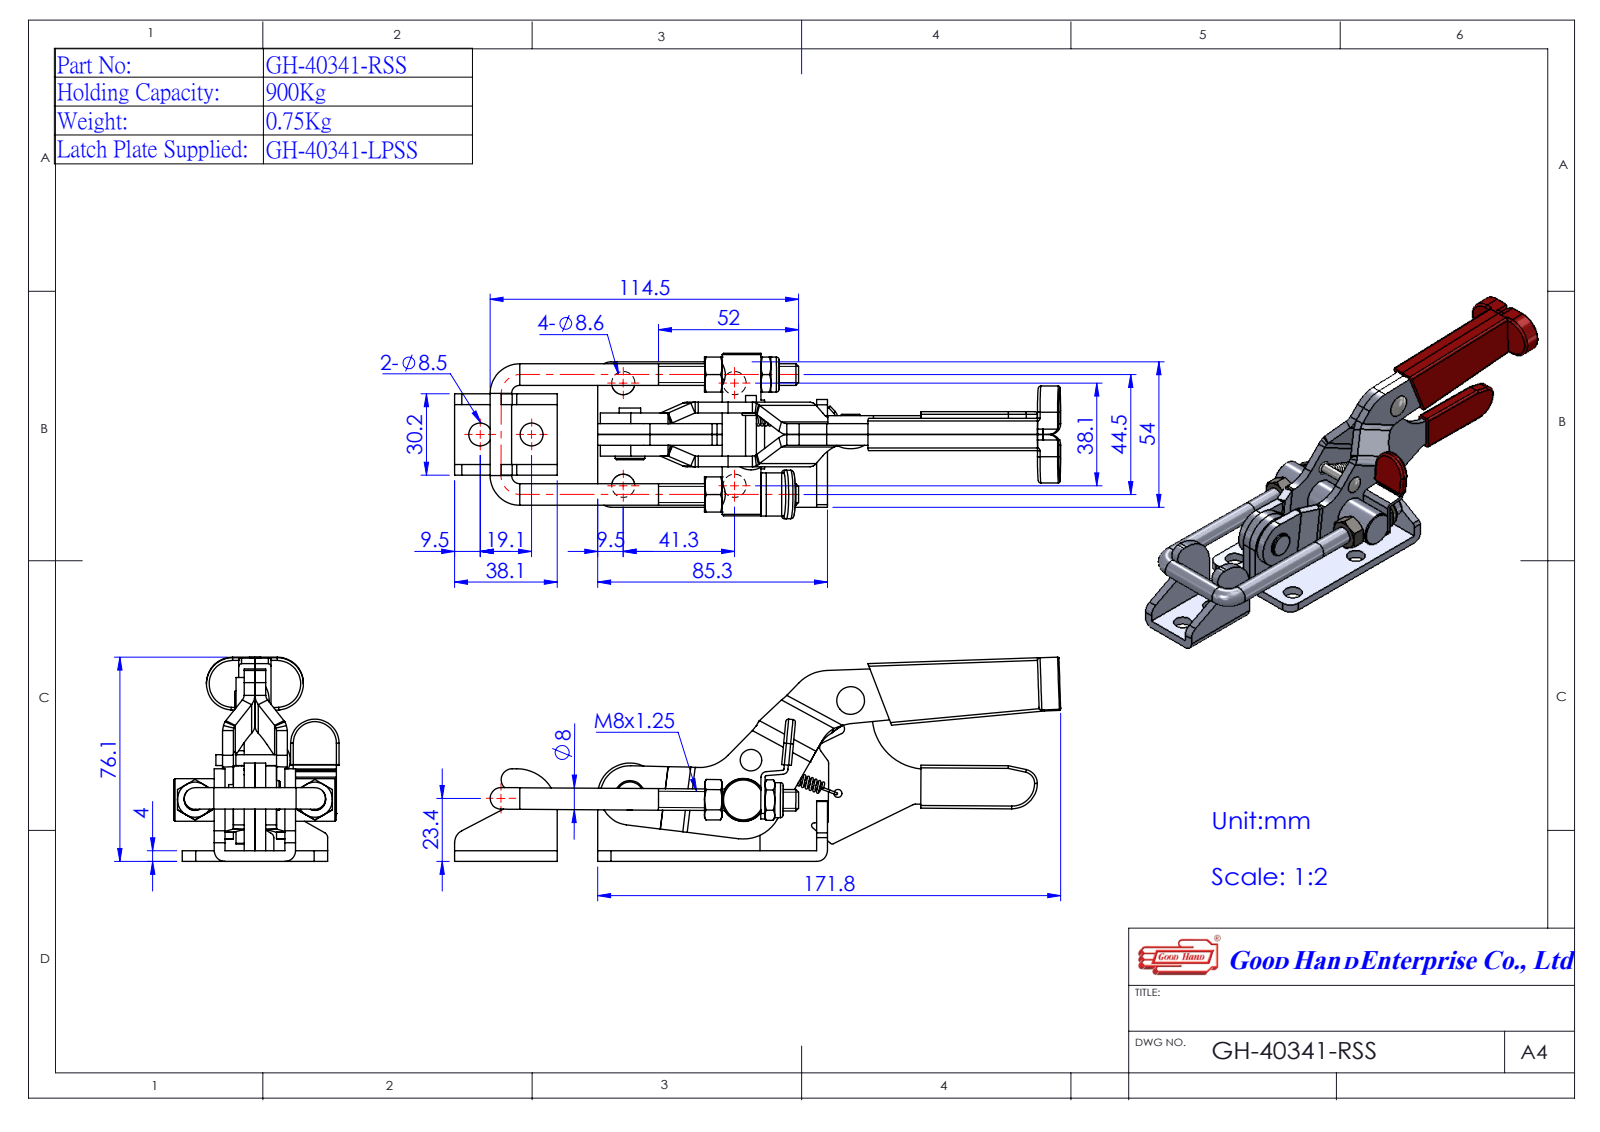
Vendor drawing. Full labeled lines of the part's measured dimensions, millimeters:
Part name (STEP PRODUCT): 140341LP-1^GH-40341-R(簡化); GH-40341-RSS(簡化); Group1^GH-40341-R(簡化); Group2^GH-40341-R(簡化) (+2 more)
STEP written by: SolidWorks 2016 (AUTOMOTIVE_DESIGN)
Units: millimetres
Bodies: 8 solids, 455 faces (205 planar, 149 cylindrical, 101 other)
Overall size (bounding box): 225.03 × 75.85 × 61.4
Volume: 112 863 mm³ · Surface area: 56 128 mm²
Round holes (diameter × count): ⌀8 ×5, ⌀6.8 ×4, ⌀8.6 ×4, ⌀8.3 ×3, ⌀8.5 ×2, ⌀9.43 ×2, ⌀6 ×1, ⌀6.35 ×1, ⌀15.8 ×1
Round bosses / shafts (diameter × count): ⌀8 ×3, ⌀13 ×2, ⌀11 ×1, ⌀6.3 ×1
Partial cylindrical surfaces — rounded edges, fillets, slot ends (radius × count): R5 ×8, R2 ×6, R15 ×6, R9 ×5, R0.1 ×4, R4.1 ×4, R0.5 ×3, R1 ×2
Main face-to-face distances: 4, 2, 8, 12, 16, 23.1, 3.1, 7.1, 19.1, 1
Hole centre spacings: 44.5, 38.1, 38.97, 41.3, 56.19, 56.41, 77.67, 96.3
